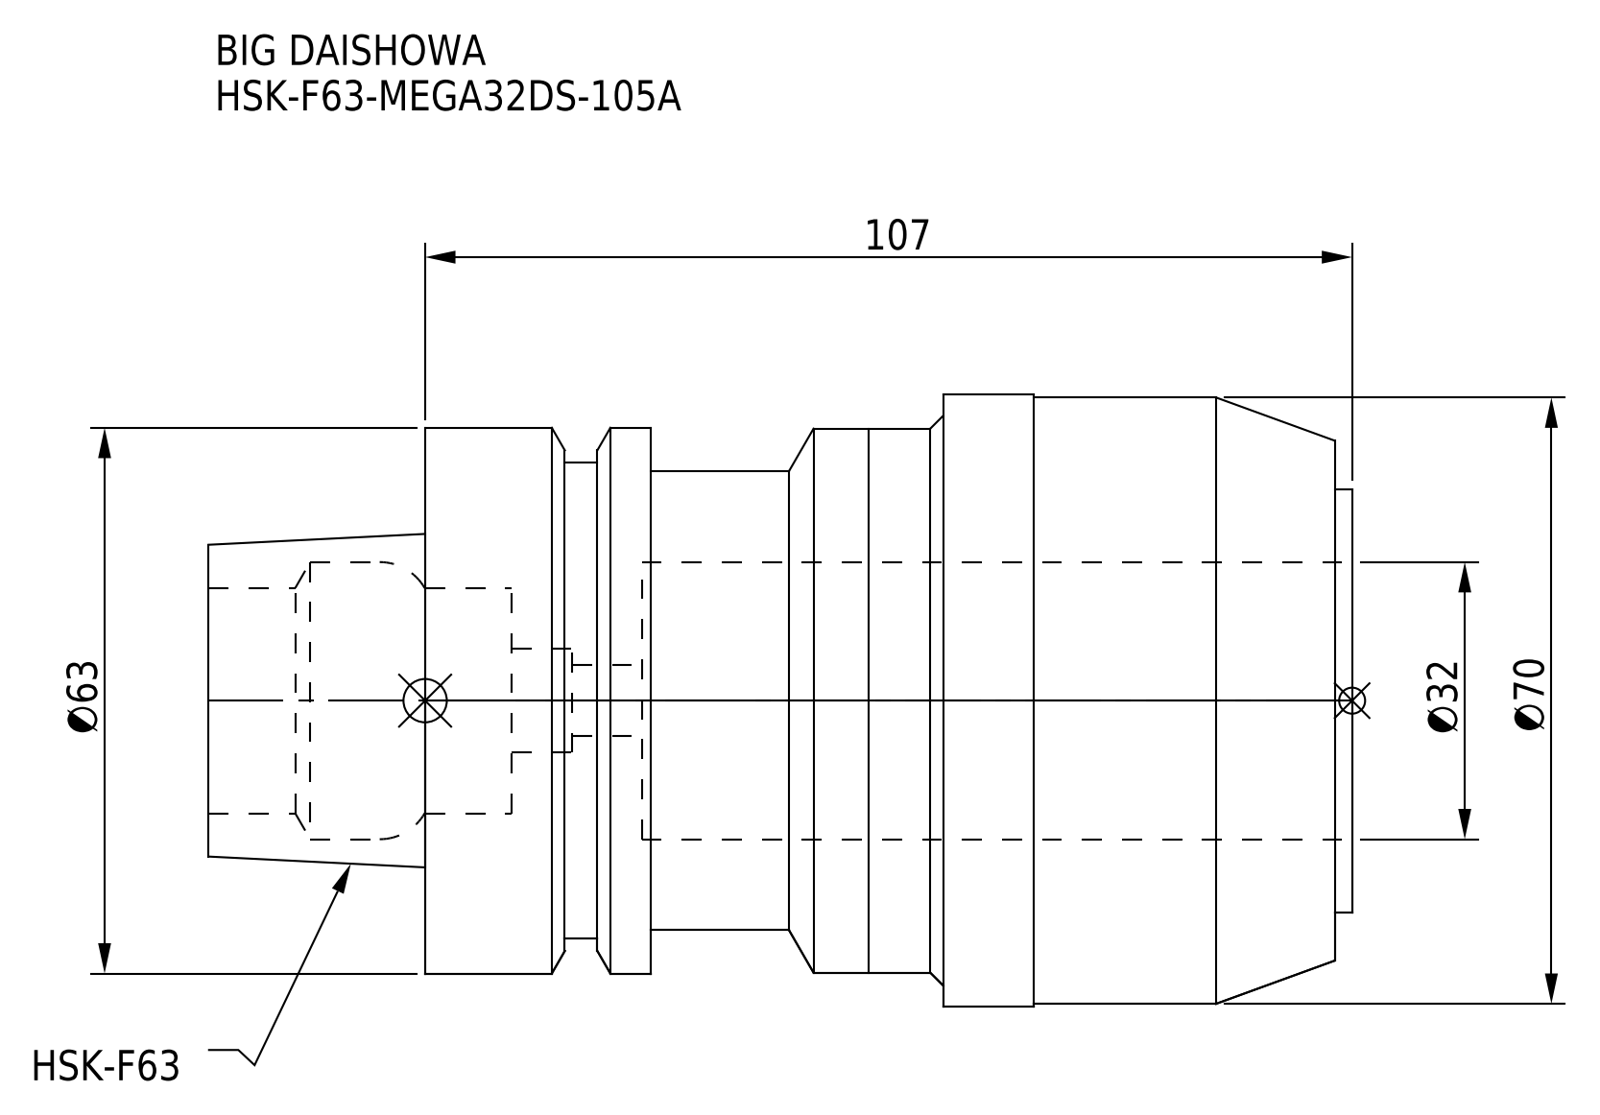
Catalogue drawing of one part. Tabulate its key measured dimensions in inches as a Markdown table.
| quantity | value |
| --- | --- |
| part name | HSK-F63-MEGA32DS-105A |
| STEP written by | CREO PARAMETRIC BY PTC INC, 2016380 (AUTOMOTIVE_DESIGN) |
| units | inches |
| bodies | 1 solid, 58 faces (12 planar, 30 cylindrical, 16 other) |
| overall size | 5.197 × 2.783 × 2.783 |
| volume | 16.86 in³ |
| surface area | 70.23 in² |
| round holes (diameter × count) | 0.325 × 1, 0.472 × 1, 1.024 × 1, 1.26 × 1 |
| round bosses / shafts (diameter × count) | 2.783 × 1, 2.756 × 1, 2.48 × 1, 2.472 × 1, 2.165 × 1, 2.087 × 1, 1.925 × 1 |
| main face-to-face distances | 0.984, 4.213, 0.079, 4.134, 3.189, 3.11, 1.024, 3.228, 3.15, 0.039 |
